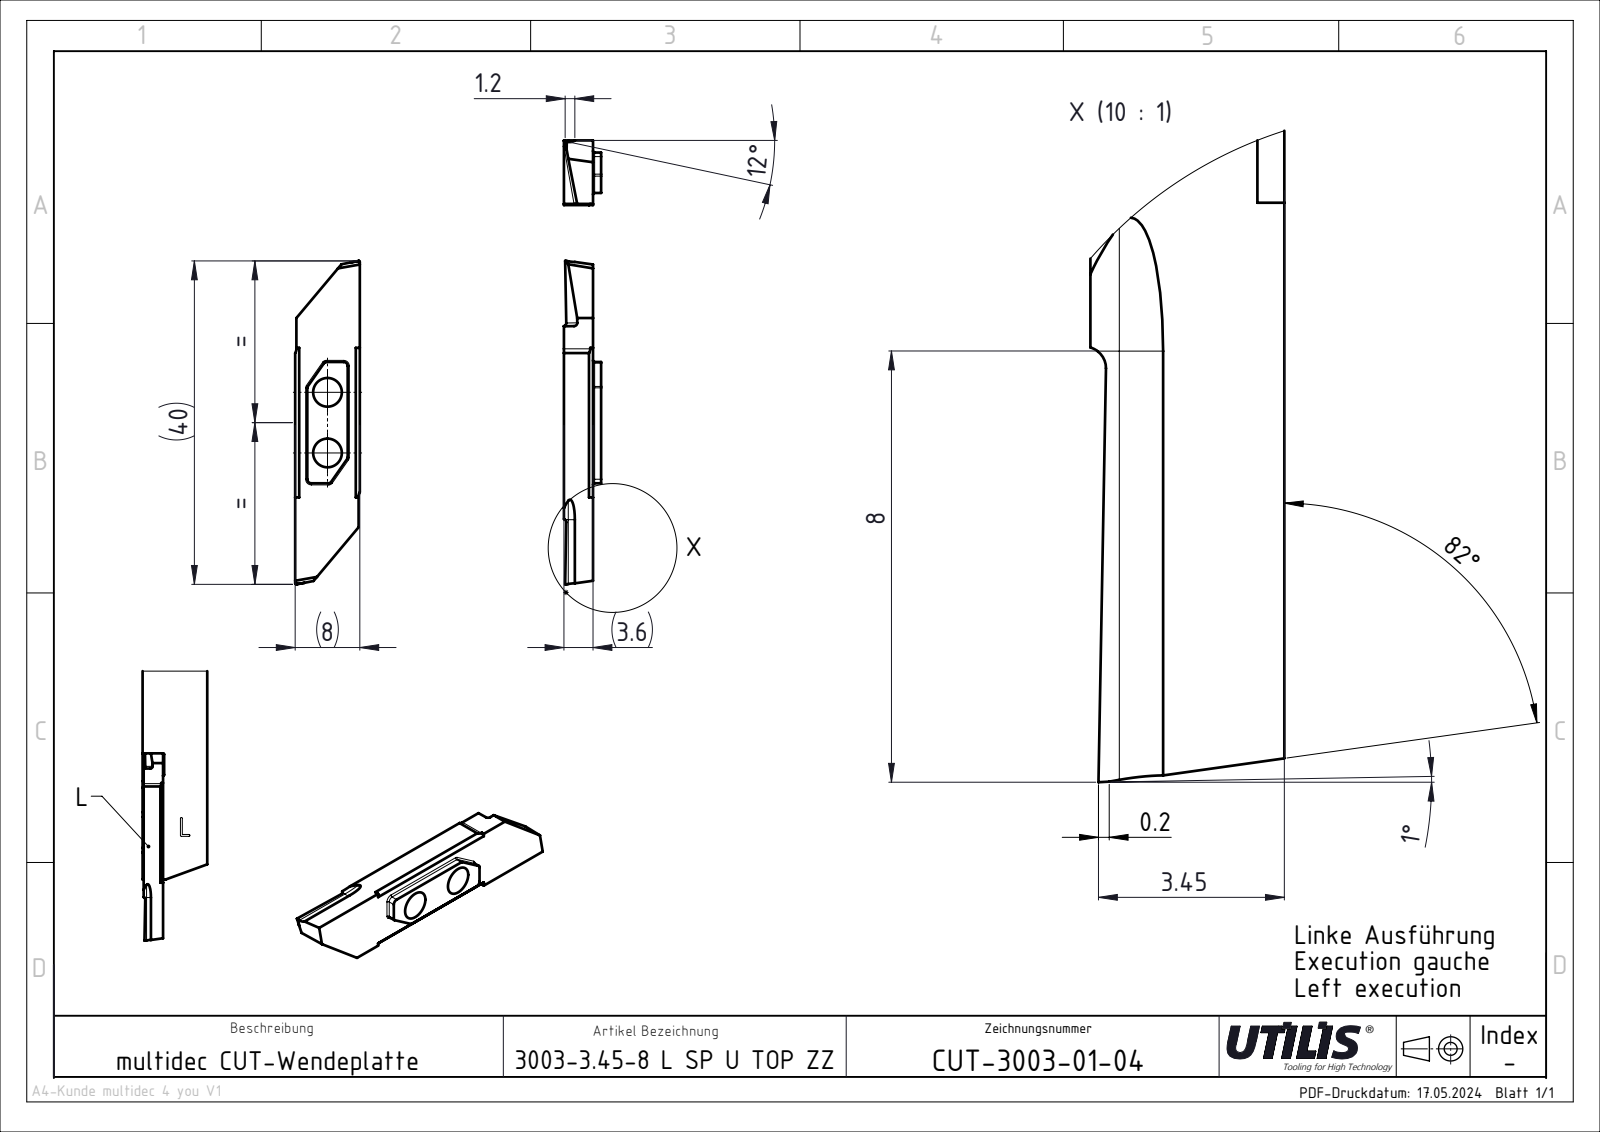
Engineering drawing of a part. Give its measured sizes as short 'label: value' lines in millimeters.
name: CUT-3003 SP U TOP; ASME Y14.5
written by: SolidWorks 2023 SP4 || FormatWorks Professional (AP242_MANAGED_MODEL_BASED_3D_ENGINEERING_MIM_LF)
unit: mm
bodies: 1 solid, 28 faces (20 planar, 8 cylindrical, 0 other)
size: 40 × 8 × 3.6
volume: 891 mm³; area: 887 mm²
holes: 2× ⌀3.55
rounds: 2× R0.4, 2× R1
face distances: 3.6, 8, 22.54, 7.85, 7.7, 18.5
hole spacings: 7.49
